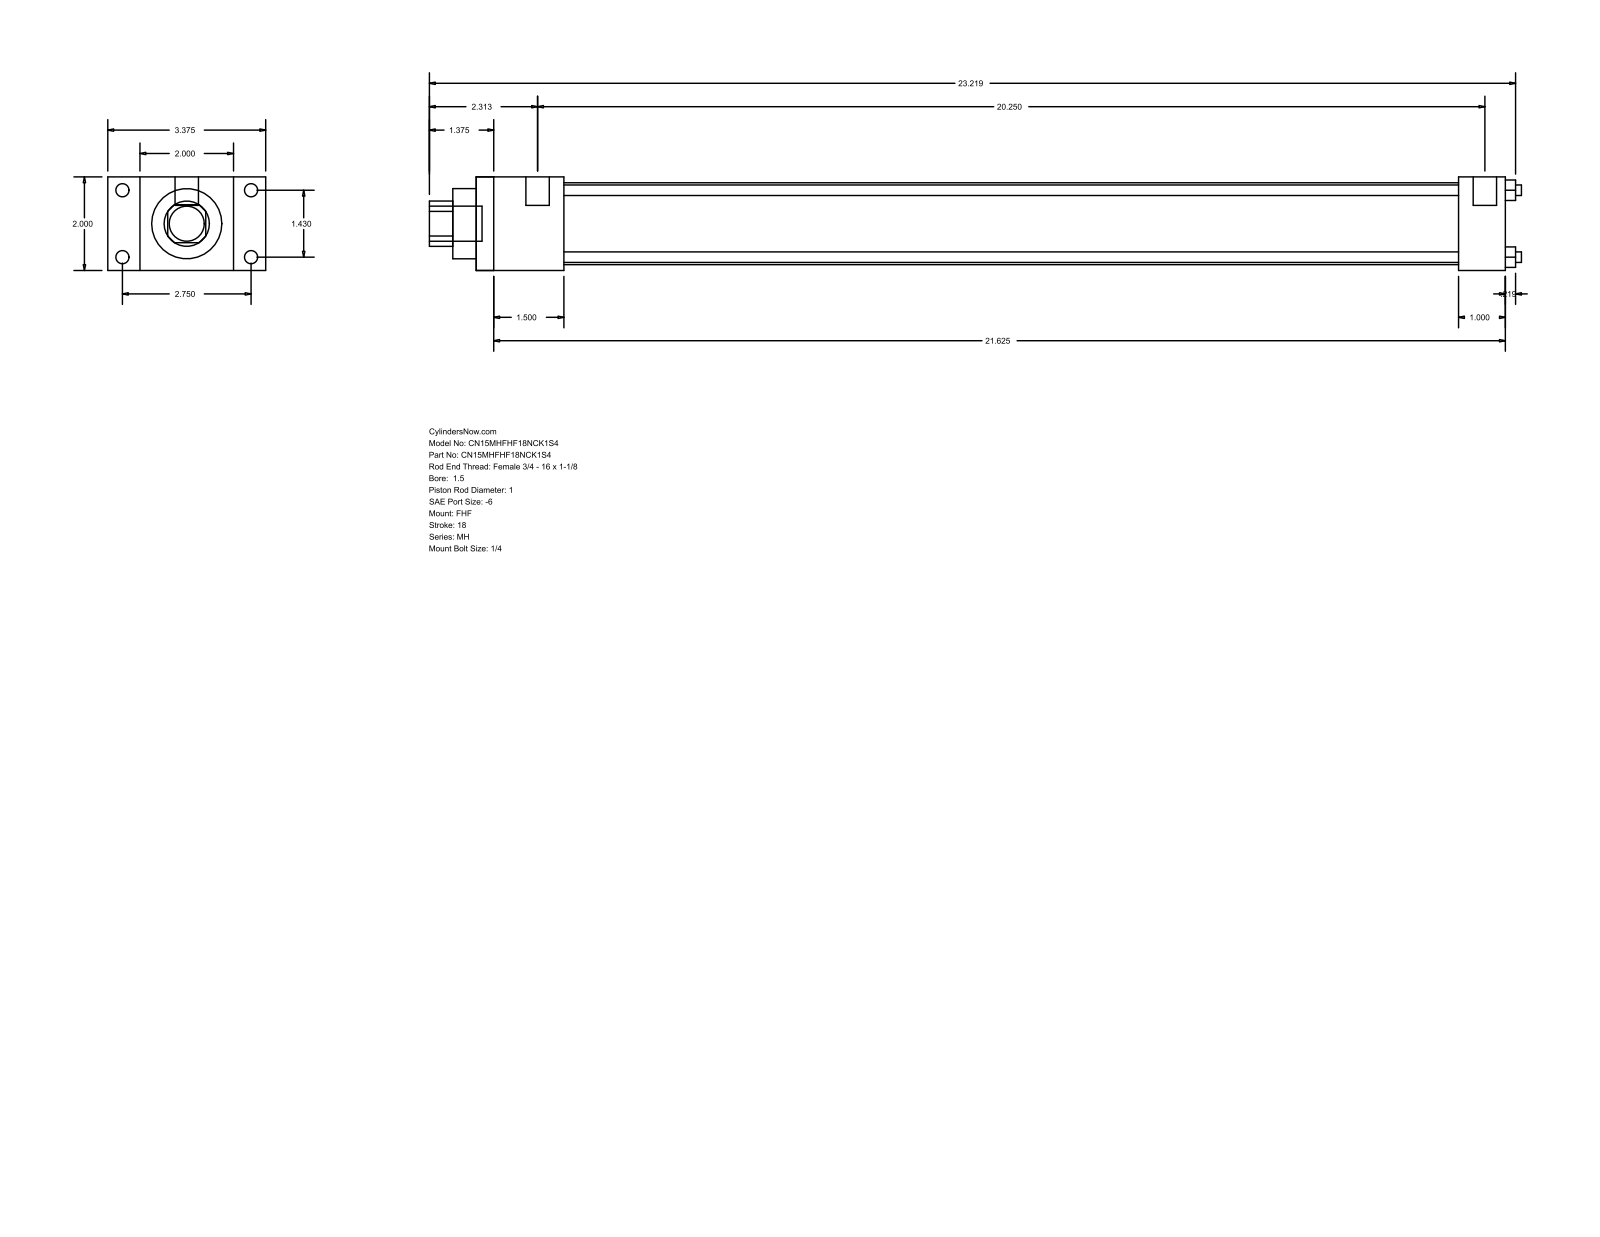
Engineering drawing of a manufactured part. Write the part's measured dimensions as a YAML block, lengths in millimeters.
part_name: "MH_FHF__0150_1"
step_written_by: "GSSL Pune (CONFIG_CONTROL_DESIGN)"
units: millimeters
bodies: {solids: 0, faces: 88, planar: 60, cylindrical: 28, other: 0}
overall_size: [592.93, 85.72, 50.8]
round_holes:
  - {diameter: 5.71, count: 4}
  - {diameter: 25.4, count: 1}
  - {diameter: 38.1, count: 1}
  - {diameter: 44.45, count: 1}
round_bosses_or_shafts:
  - {diameter: 7.14, count: 4}
  - {diameter: 5.56, count: 4}
  - {diameter: 12.7, count: 2}
  - {diameter: 19.05, count: 1}
partial_cylinders:
  - {radius: 12.29, count: 1}
face_to_face_distances: [50.8, 17.46, 68.26, 47.63, 85.72, 558.8, 511.17, 25.4, 533.4, 485.77]
hole_center_spacings: [25.68, 36.32, 51.36]
